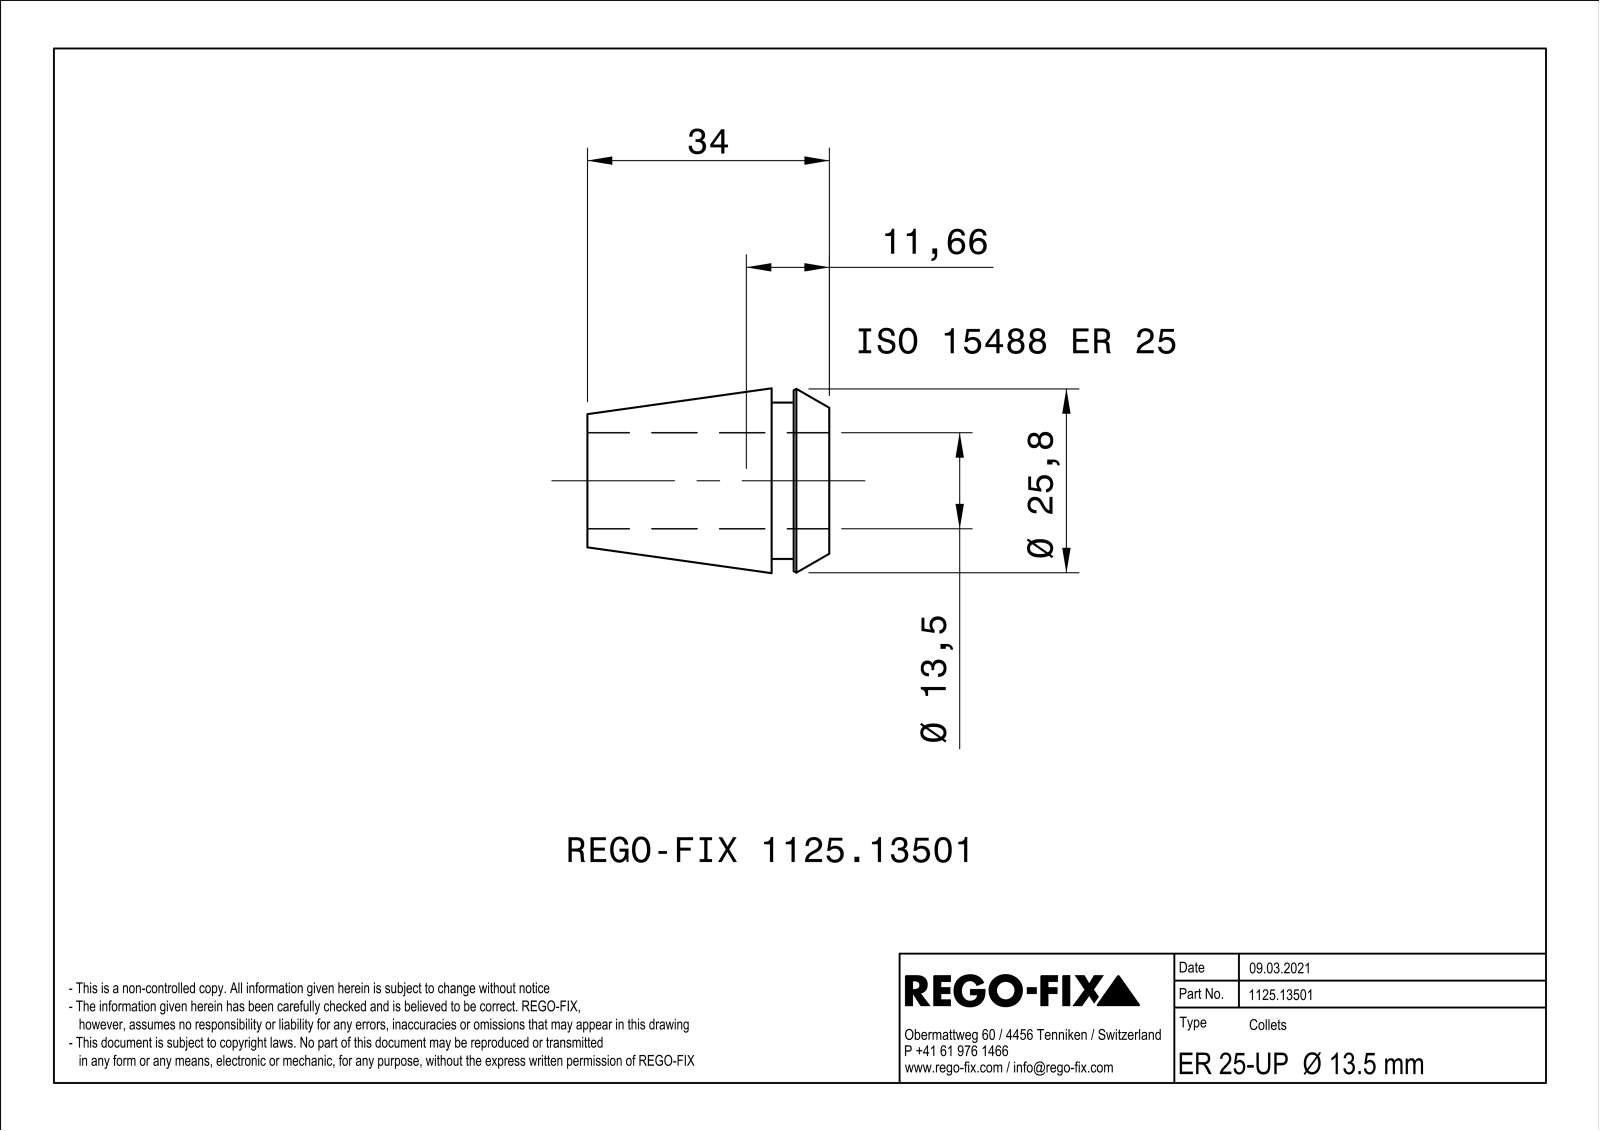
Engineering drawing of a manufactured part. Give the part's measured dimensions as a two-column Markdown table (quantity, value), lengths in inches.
| quantity | value |
| --- | --- |
| part name | NOCUT |
| STEP written by | SIEMENS PLM Software Solid Edge ST10 (AUTOMOTIVE_DESIGN) |
| units | inches |
| bodies | 1 solid, 177 faces (72 planar, 25 cylindrical, 80 other) |
| overall size | 1.339 × 1.023 × 1.023 |
| volume | 0.427 in³ |
| surface area | 12.4 in² |
| round holes (diameter × count) | 0.531 × 1 |
| round bosses / shafts (diameter × count) | 0.866 × 1 |
| partial cylindrical surfaces (radius × count) | 0.016 × 8 |
| main face-to-face distances | 0.031, 0.319, 0.197, 0.122, 1.339, 1.142, 1.02 |
